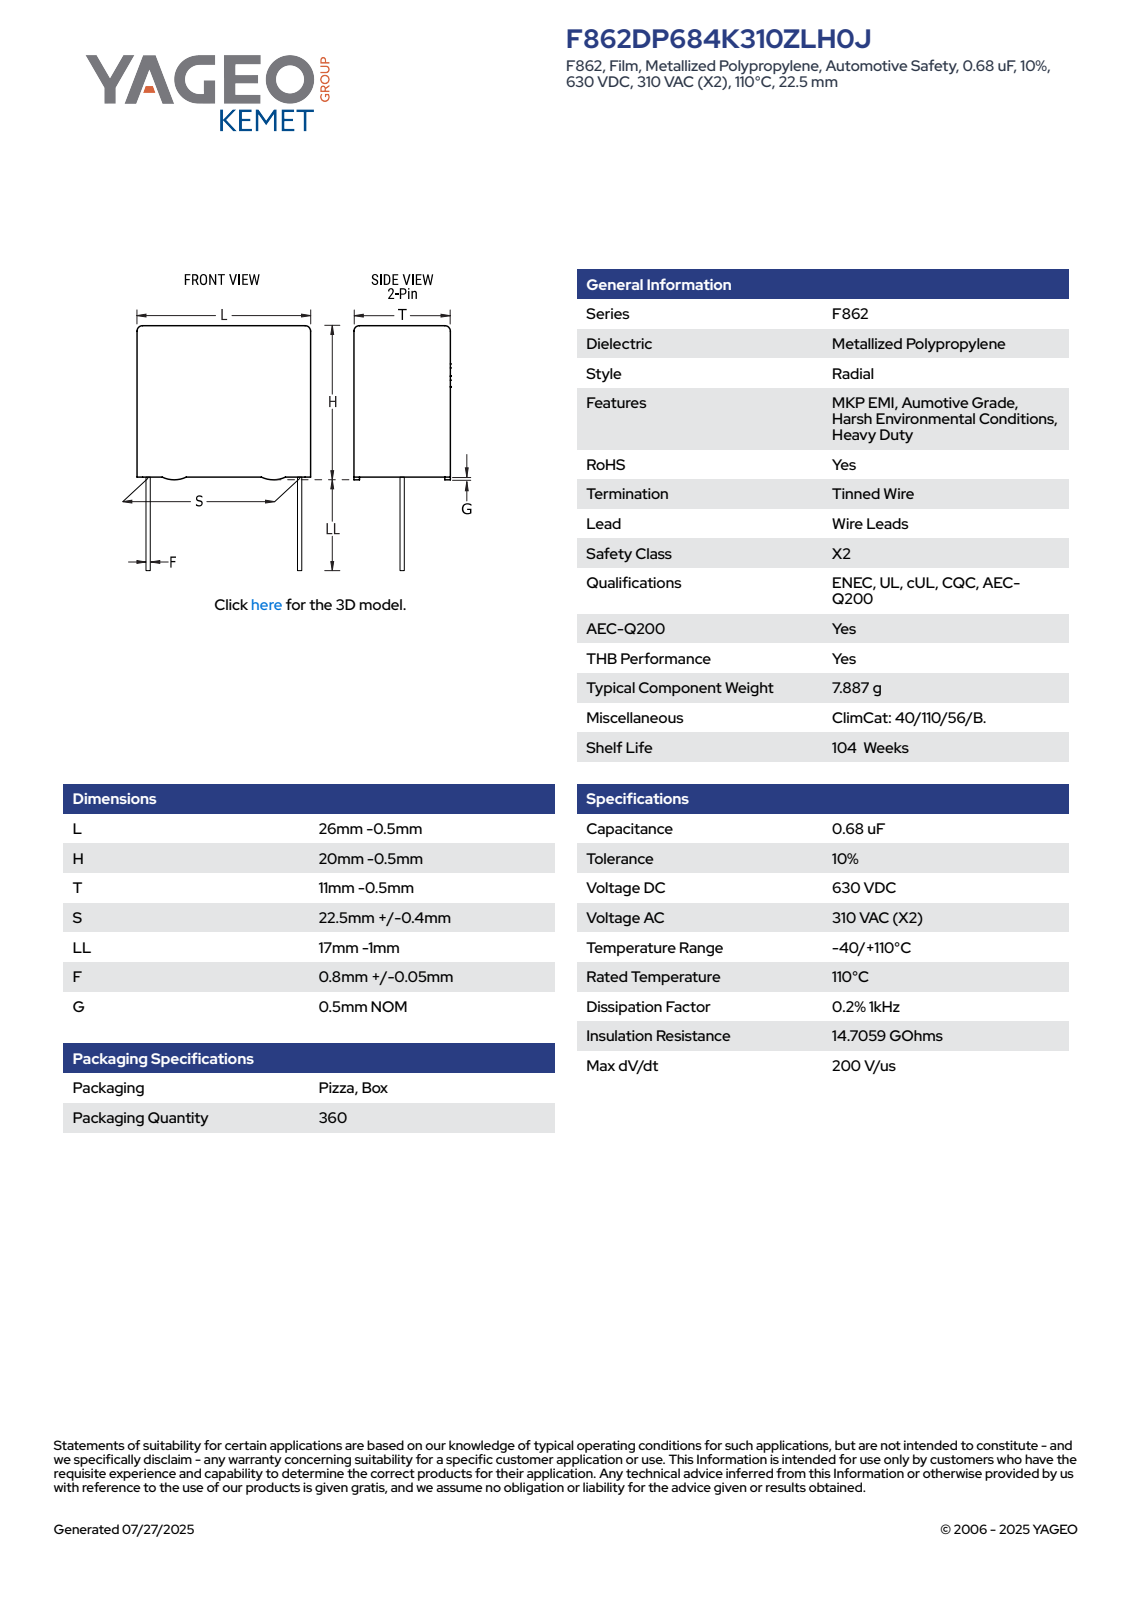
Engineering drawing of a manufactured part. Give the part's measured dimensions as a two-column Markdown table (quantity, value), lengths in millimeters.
| quantity | value |
| --- | --- |
| part name | CFR_RBG_26X20X11_L25.5H19.5T10.5S22.5LL16F0.85G0.5 |
| STEP written by | SolidWorks 2014 (AUTOMOTIVE_DESIGN) |
| units | millimeters |
| bodies | 4 solids, 89 faces (81 planar, 8 cylindrical, 0 other) |
| overall size | 35.5 × 25.5 × 10.51 |
| volume | 5 107 mm³ |
| surface area | 2 064 mm² |
| round bosses / shafts (diameter × count) | 0.85 × 2 |
| partial cylindrical surfaces (radius × count) | 0.5 × 4 |
| main face-to-face distances | 10.5, 19, 25.5, 10.51, 0.5, 19.5, 0.6, 9.9, 0.61, 9.3 |
